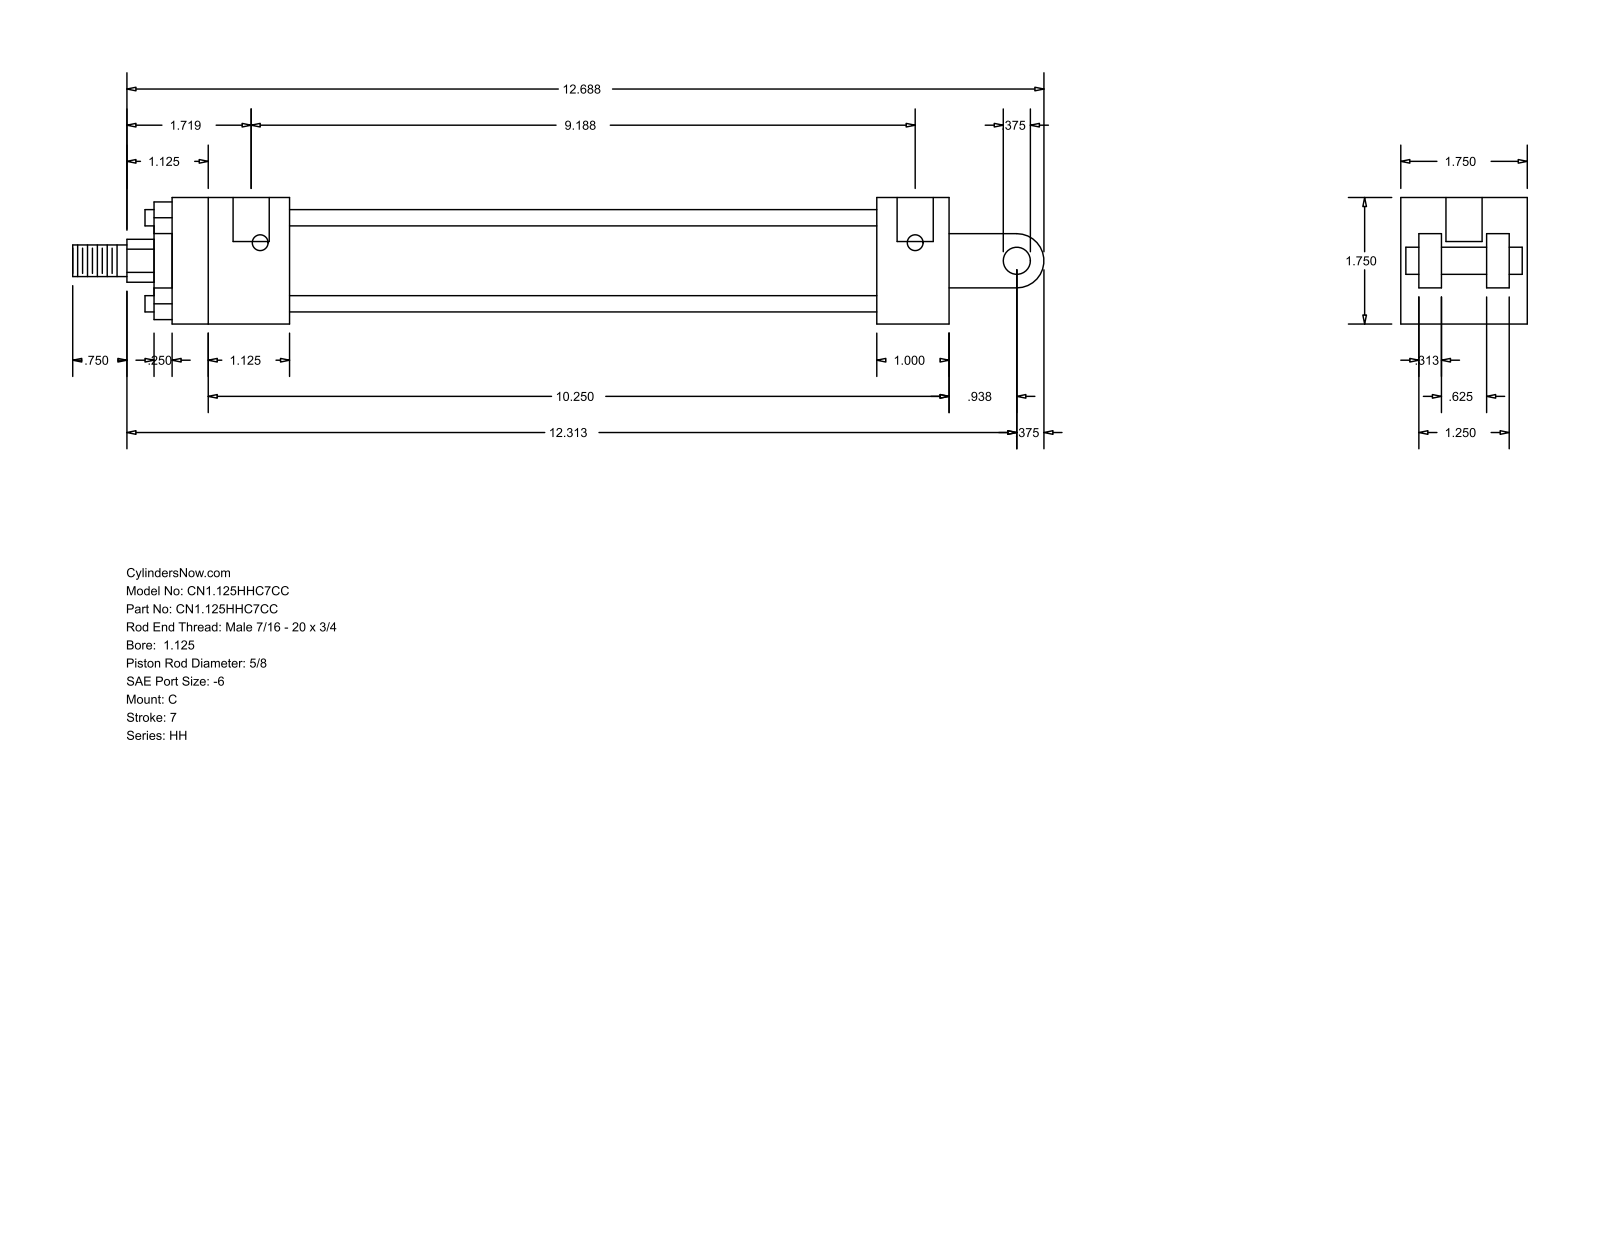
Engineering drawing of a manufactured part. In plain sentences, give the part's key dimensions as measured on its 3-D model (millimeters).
The part is named "HH_C__0112_0.625". Its 3-D file was written by "GSSL Pune (CONFIG_CONTROL_DESIGN)". It is 0 solids with 99 faces: 70 planar, 29 cylindrical and 0 other. Overall it measures 341.31 by 44.45 by 44.45 millimeters. Round holes: 4 of diameter 5.56, 2 of diameter 12.7. Round bosses or shafts: 4 of diameter 5.71, 1 of diameter 34.92, 1 of diameter 28.57, 1 of diameter 15.88, 1 of diameter 11.11, 1 of diameter 9.53. Partial cylindrical surfaces (rounded edges, fillets, slot ends): 1 of radius 7.54, 1 of radius 9.53. The main face-to-face distances are 44.46, 6.35, 31.76, 14.29, 30.17, 38.11, 7.94, 23.82, 12.7, 41.27. The hole center spacings are 230.19, 3.17, 233.36.
